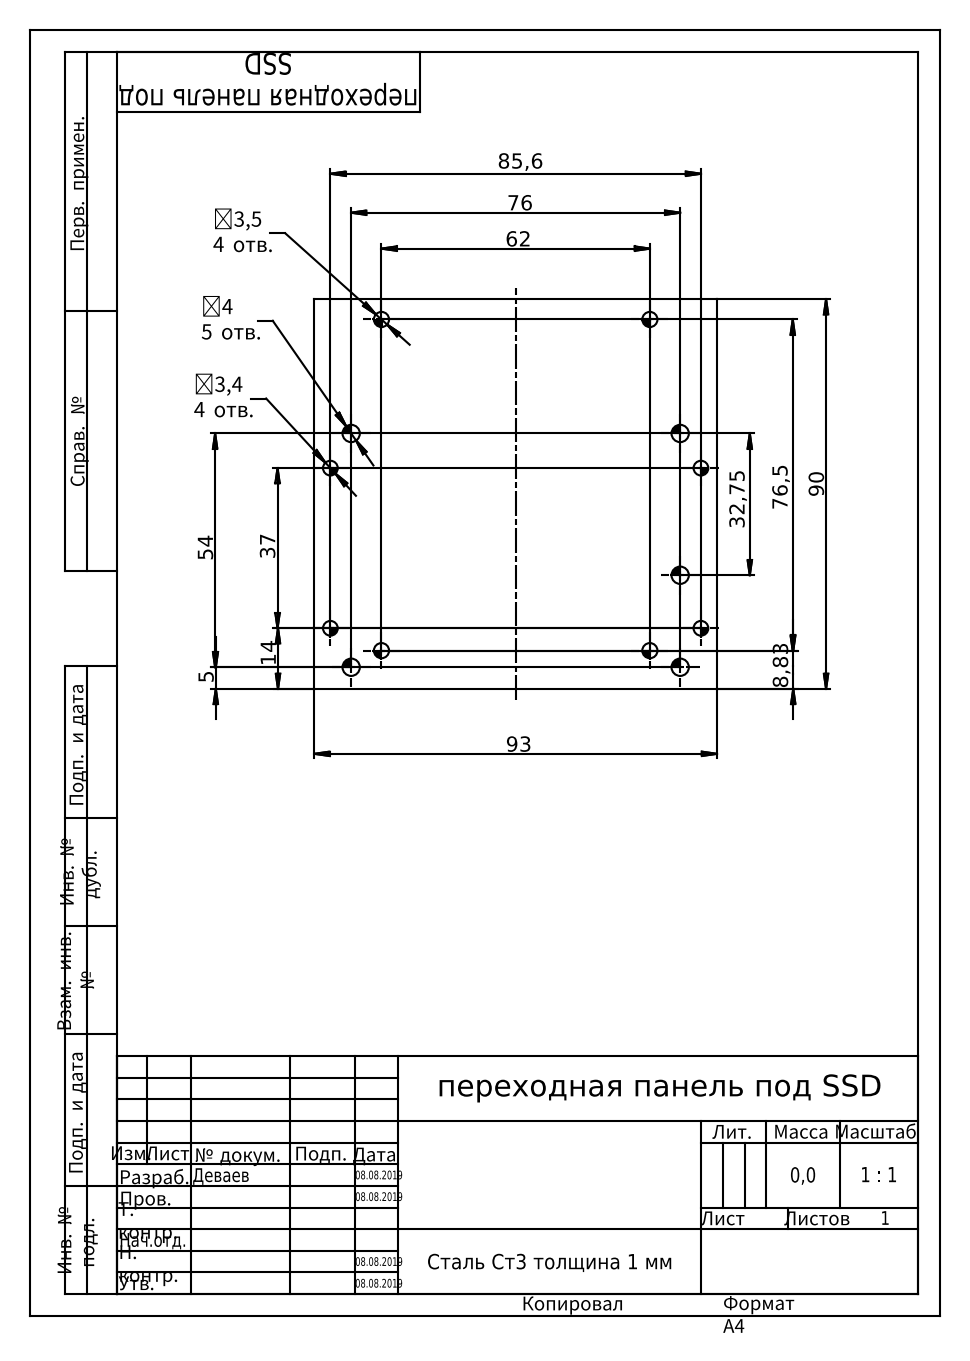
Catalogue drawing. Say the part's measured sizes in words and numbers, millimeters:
The part is named "переходная панель под SSD". Its 3-D file was written by "Autodesk Inventor 2019 (AUTOMOTIVE_DESIGN)". It is 1 solid with 19 faces: 6 planar, 13 cylindrical and 0 other. Overall it measures 93 by 90 by 1 millimeters. Its volume is 8 232 cubic millimeters and its surface area 16 980 square millimeters. Round holes: 5 of diameter 4, 4 of diameter 3.4, 4 of diameter 3.5. The main face-to-face distances are 1, 90, 93. The hole center spacings are 7.98, 9.33, 10.2, 12.88, 27.24, 36.3, 37, 43.79.
